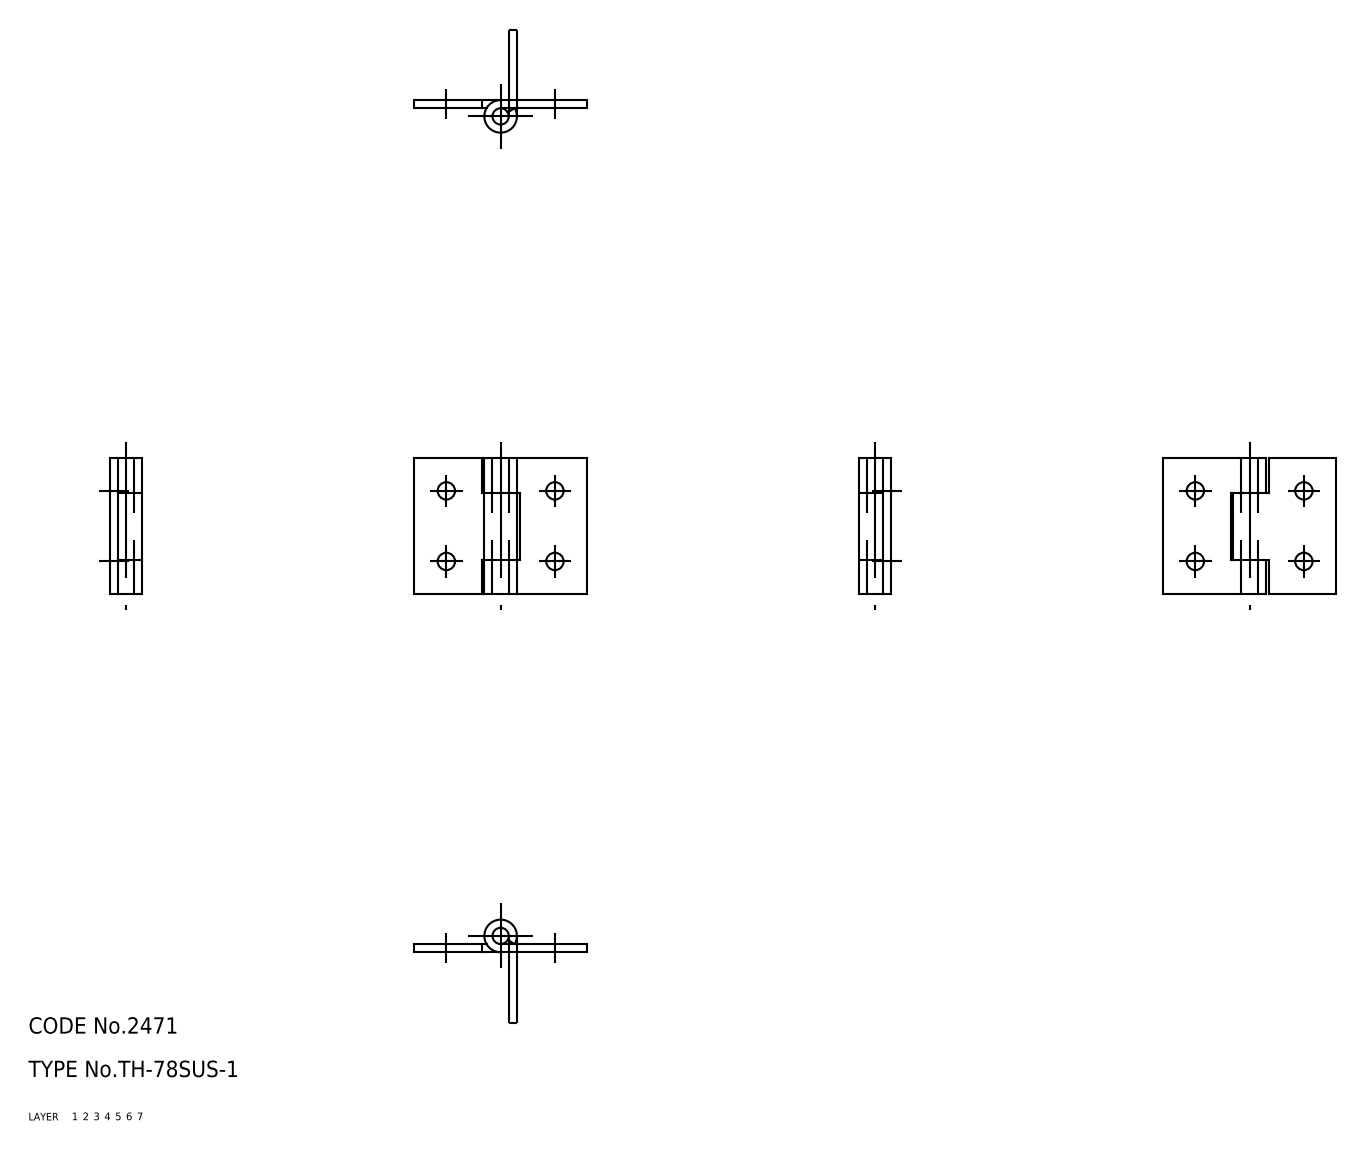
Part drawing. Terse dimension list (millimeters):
name: hinge piece_B; hinge piece_A; shaft; TH_78SUS_1_17033_36
written by: CADfix (AUTOMOTIVE_DESIGN)
unit: mm
bodies: 3 solids, 38 faces (0 planar, 0 cylindrical, 38 other)
size: 32 × 25 × 6
volume: 1 638 mm³; area: 2 620 mm²
